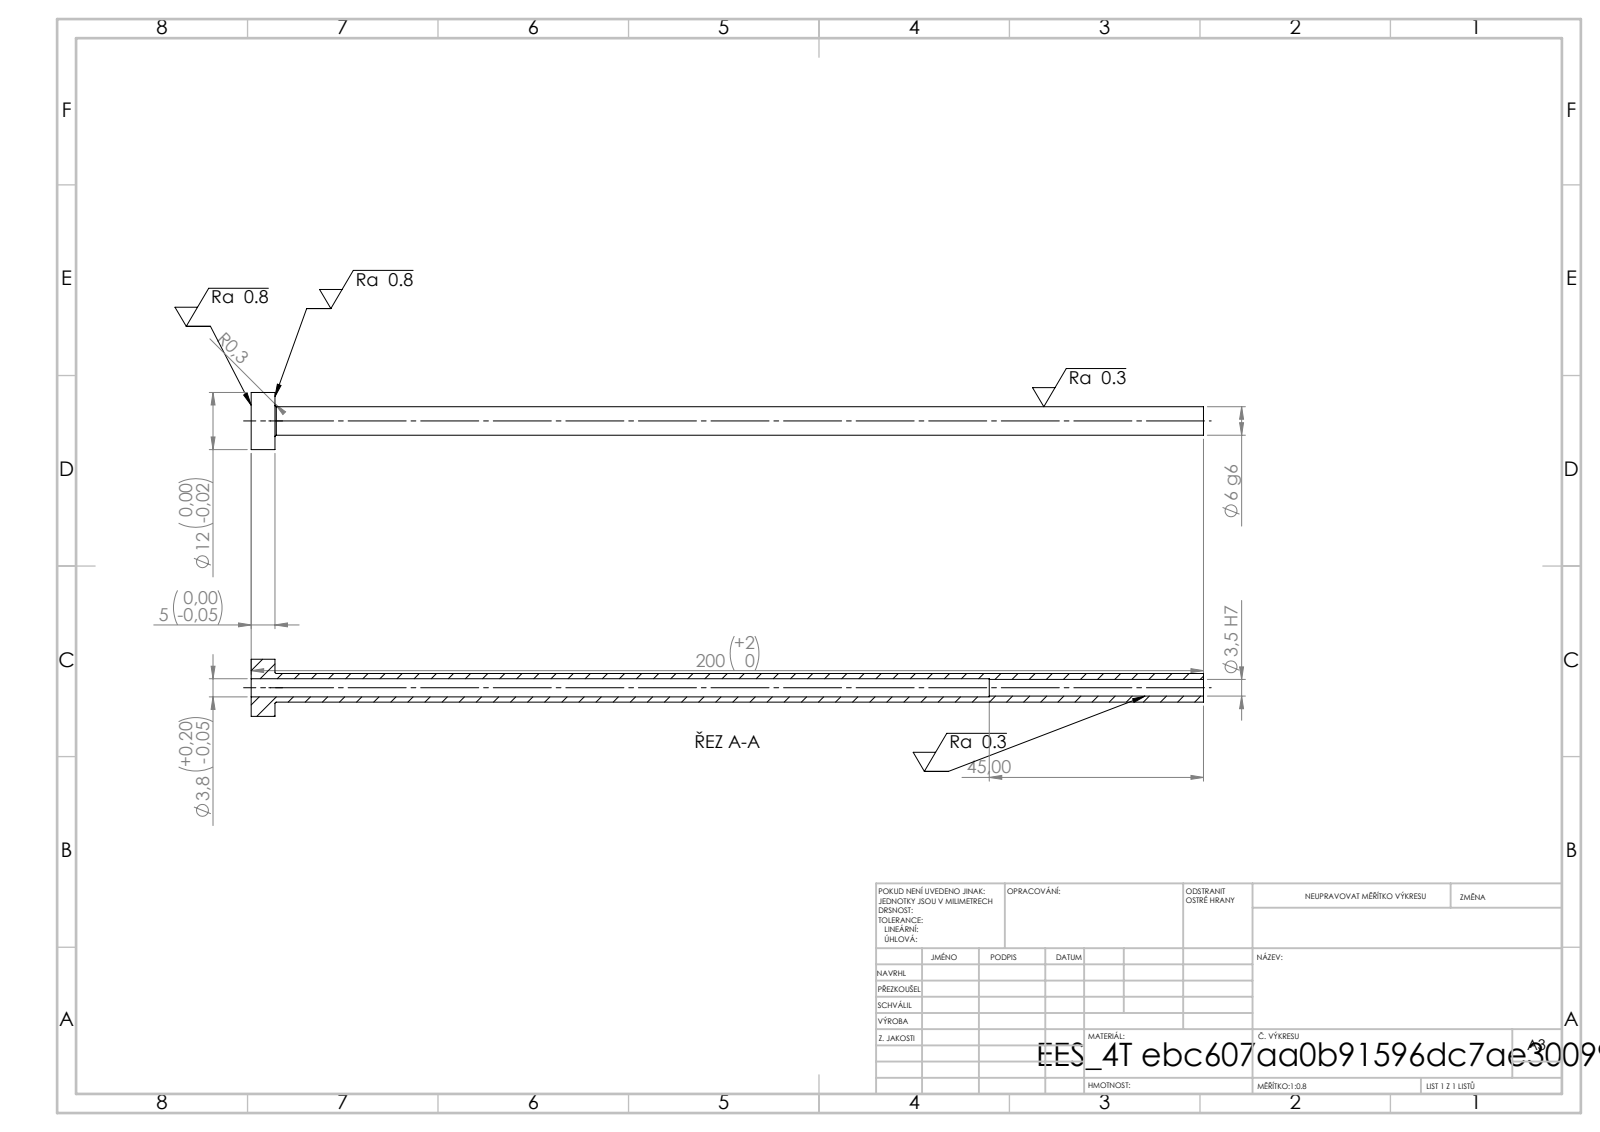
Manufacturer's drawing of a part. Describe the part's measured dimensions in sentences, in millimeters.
Its 3-D file was written by "SolidWorks 2019 (CONFIG_CONTROL_DESIGN)". It is 1 solid with 14 faces: 4 planar, 8 cylindrical and 2 other. Overall it measures 200 by 12 by 12 millimeters. Its volume is 3 889 cubic millimeters and its surface area 6 414 square millimeters. Round holes: 1 of diameter 3.5, 1 of diameter 3.8. Round bosses or shafts: 1 of diameter 12, 1 of diameter 6. The main face-to-face distances are 5, 200, 195, 155, 150, 45.
